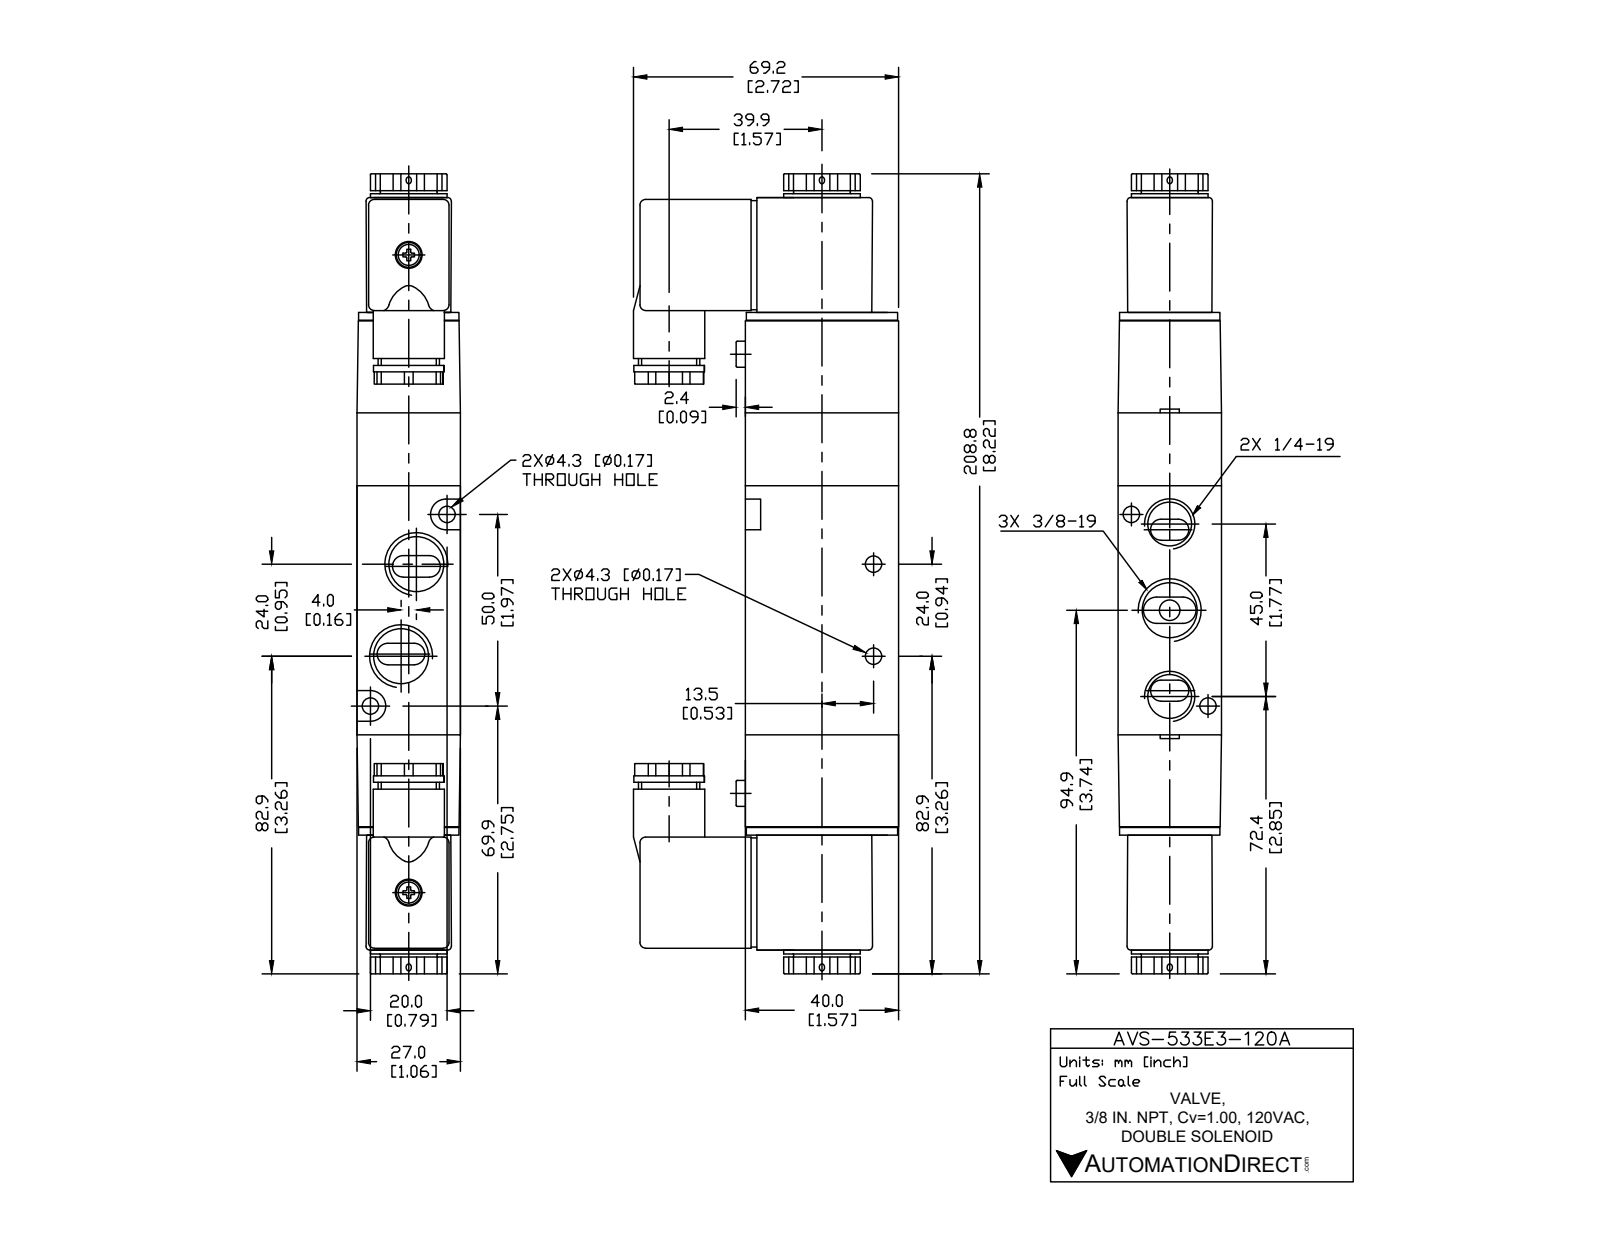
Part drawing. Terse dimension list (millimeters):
name: AVS-533E3-120A
written by: SolidWorks 2015 (CONFIG_CONTROL_DESIGN)
unit: mm
bodies: 5 solids, 272 faces (127 planar, 111 cylindrical, 34 other)
size: 208.8 × 69.2 × 27
volume: 221 817 mm³; area: 45 967 mm²
holes: 4× ⌀4.3, 3× ⌀14.27, 2× ⌀11.13, 1× ⌀9.3
bosses: 2× ⌀6.7, 1× ⌀20, 1× ⌀18.6, 1× ⌀18.4, 1× ⌀16, 1× ⌀14.8
rounds: 18× R1.5, 12× R3, 10× R1, 8× R0.5
face distances: 27, 3, 24, 40, 84, 23.22, 21, 29.5, 0.5, 166.4
hole spacings: 10.31, 10.69, 12.17, 15.26, 22.5, 26.93, 34.56, 38.9
